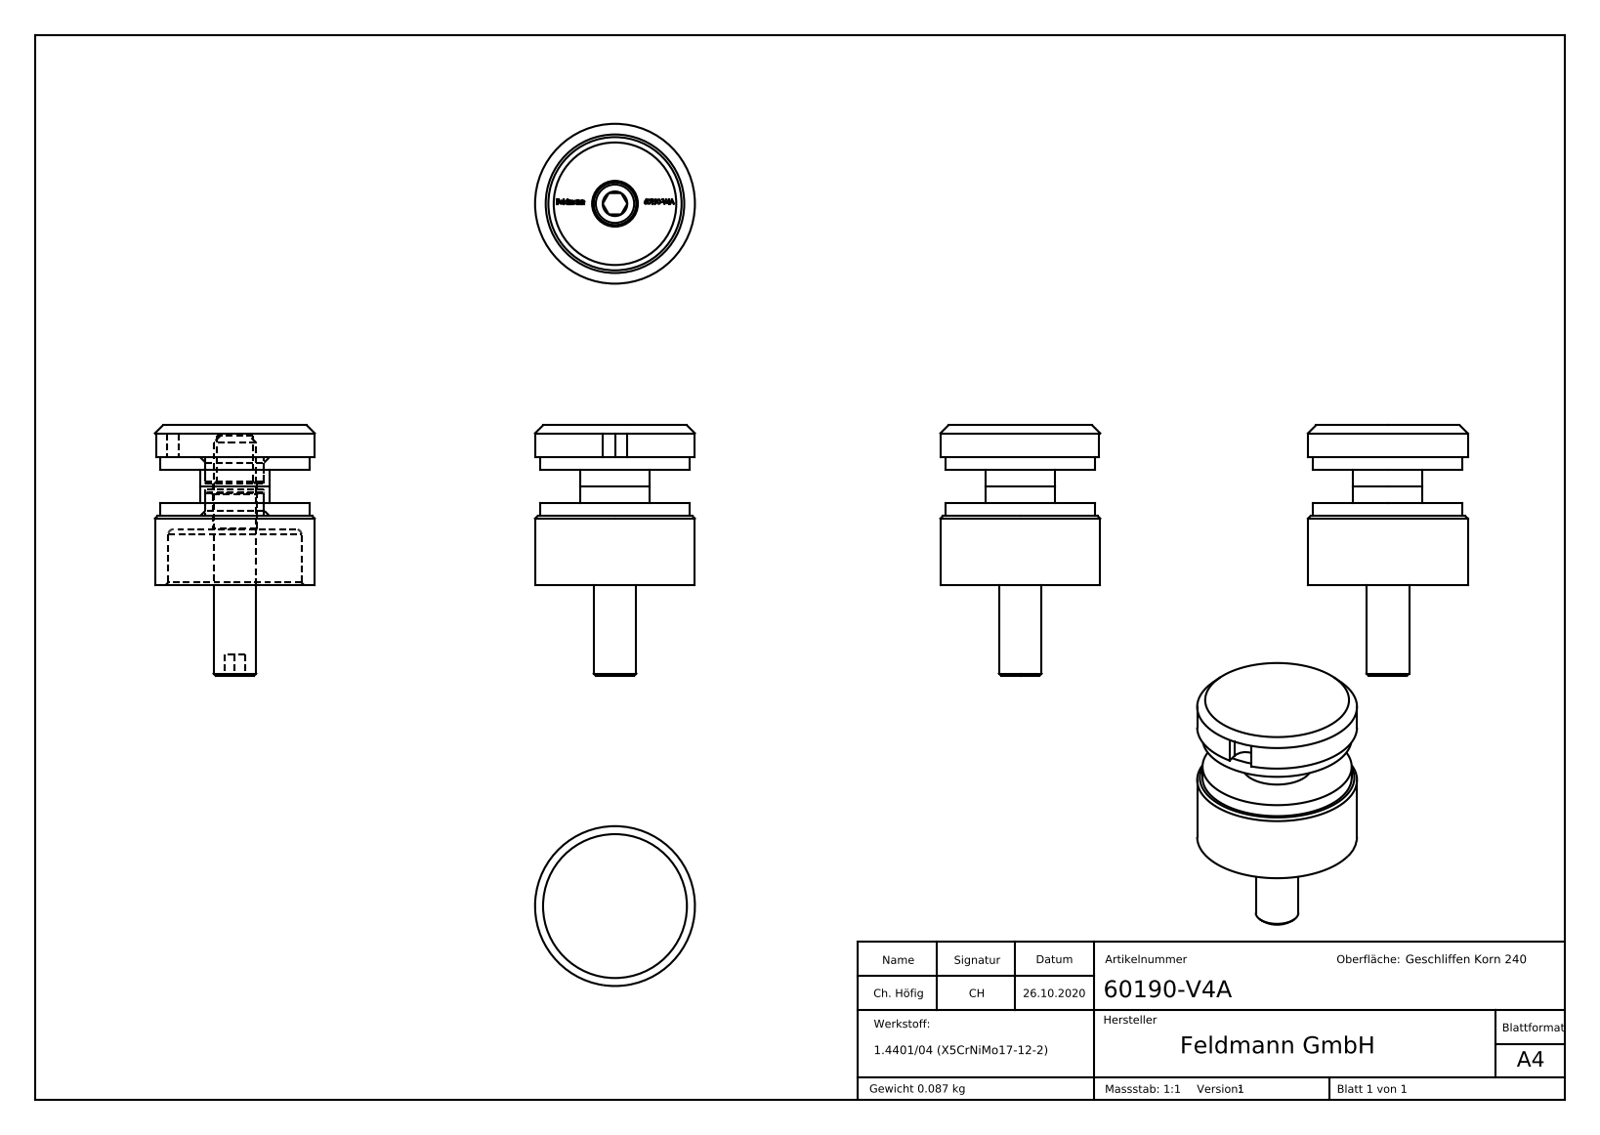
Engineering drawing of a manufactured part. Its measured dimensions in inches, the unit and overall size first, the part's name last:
Units: inches
Overall size (bounding box): 1.85 × 1.181 × 1.181
Round holes (diameter × count): ⌀0.268 ×1, ⌀0.323 ×1, ⌀0.433 ×1, ⌀0.984 ×1
Round bosses / shafts (diameter × count): ⌀1.181 ×1, ⌀1.102 ×1, ⌀0.512 ×1, ⌀0.315 ×1
Partial cylindrical surfaces — rounded edges, fillets, slot ends (radius × count): R0.089 ×1
Main face-to-face distances: 0.433, 0.094, 0.339, 0.236, 0.669, 0.331, 0.244, 0.575, 0.098, 0.193
Volume: 0.806 in³ · Surface area: 16.11 in²
Bodies: 5 solids, 301 faces (155 planar, 34 cylindrical, 112 other)
Part name (STEP PRODUCT): 60190-240 Teil2; 6019X-240 Teil3; 6019X-240 Teil3_6019X-240 Teil3; 60190-V4A (+5 more)
STEP written by: SolidWorks 2018 (CONFIG_CONTROL_DESIGN)
